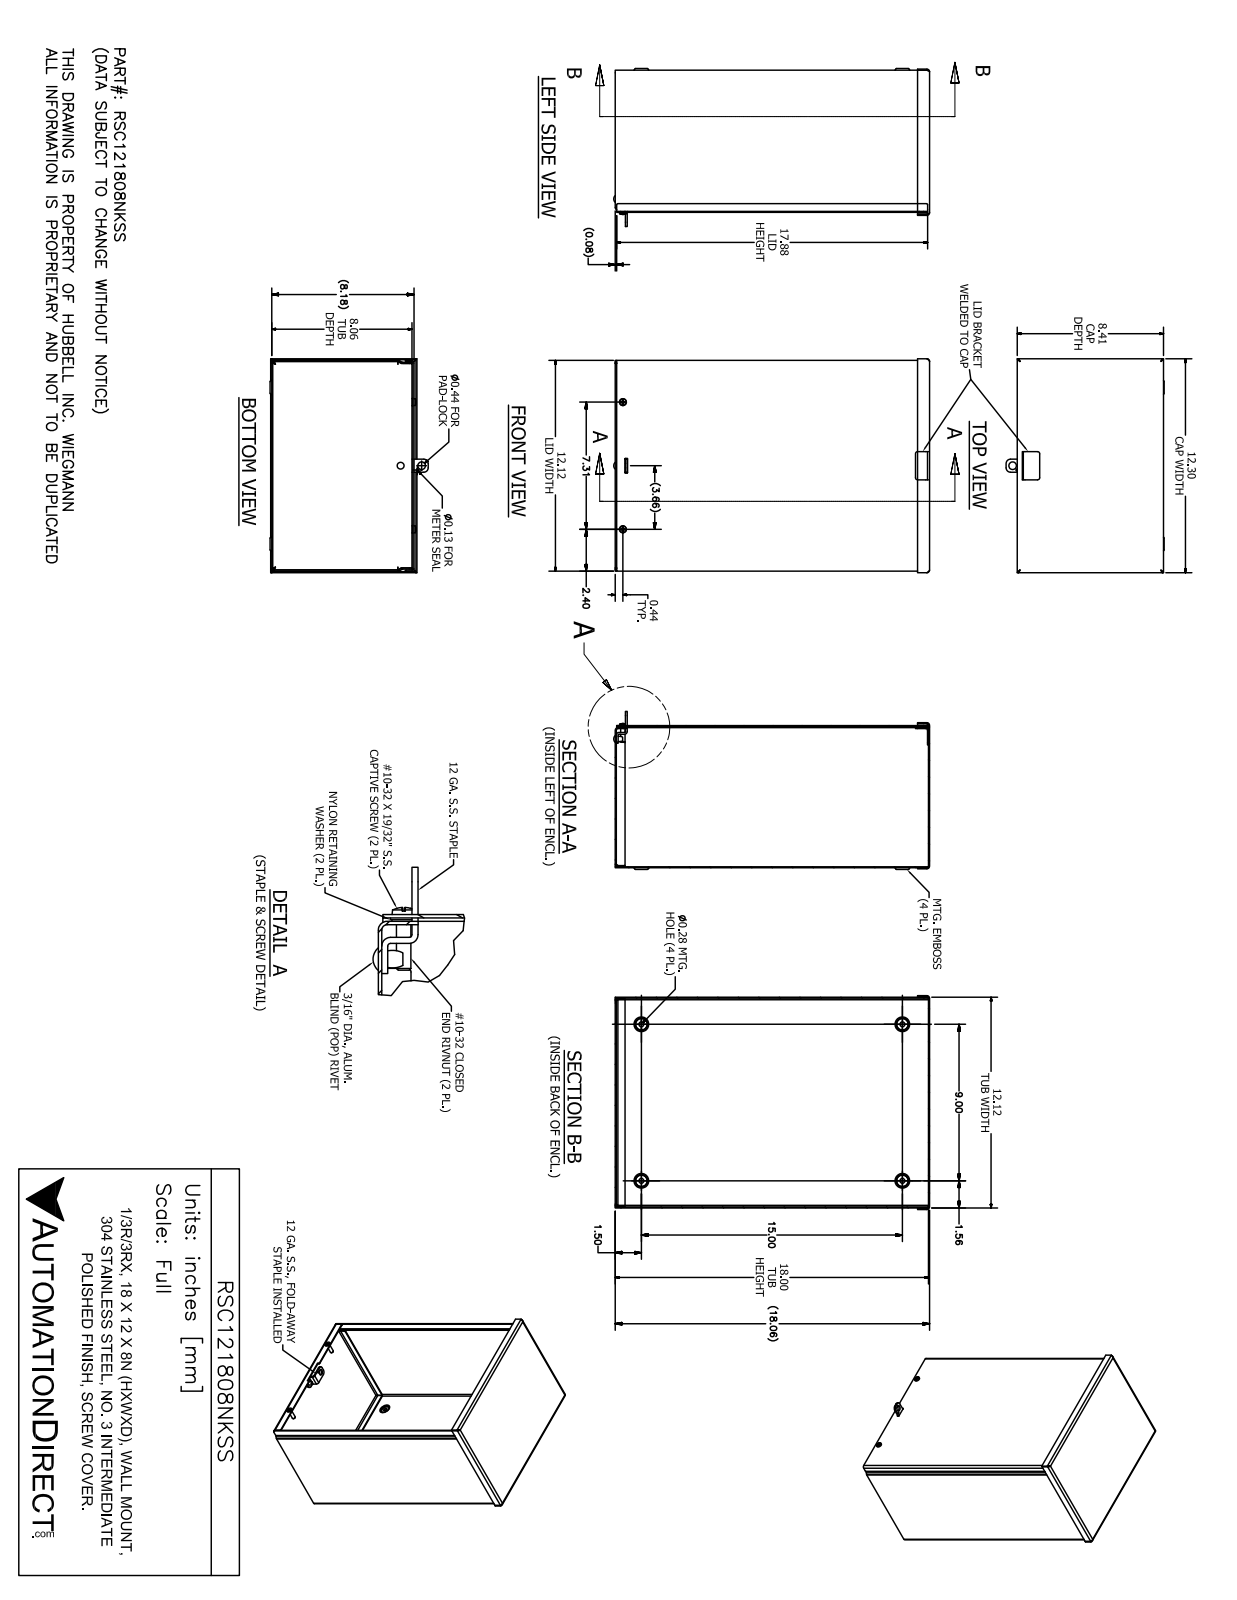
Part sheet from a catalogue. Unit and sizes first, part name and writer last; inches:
Units: inches
Overall size (bounding box): 18.149 × 12.299 × 9.084
Round holes (diameter × count): ⌀0.25 ×4, ⌀0.281 ×4, ⌀0.156 ×2, ⌀0.196 ×2, ⌀0.257 ×2, ⌀0.278 ×2, ⌀0.125 ×1, ⌀0.198 ×1, ⌀0.201 ×1, ⌀0.437 ×1
Round bosses / shafts (diameter × count): ⌀0.453 ×2, ⌀0.406 ×2, ⌀0.248 ×2, ⌀0.167 ×2, ⌀0.187 ×1
Partial cylindrical surfaces — rounded edges, fillets, slot ends (radius × count): R0.094 ×17, R0.153 ×17, R0.031 ×6, R0.125 ×4, R0.25 ×4, R0.047 ×2, R0.05 ×2, R0.062 ×2
Main face-to-face distances: 0.059, 8.117, 12.059, 8.176, 8.058, 18, 12, 12.118, 18.059, 17.941
Hole centre spacings: 1.357, 1.381, 7.313, 8.225, 8.229, 9, 15, 16.085
Volume: 58.05 in³ · Surface area: 1 982 in²
Bodies: 13 solids, 383 faces (199 planar, 99 cylindrical, 85 other)
Part name (STEP PRODUCT): RSC121808NKSS
STEP written by: SolidWorks 2017 (AUTOMOTIVE_DESIGN)
